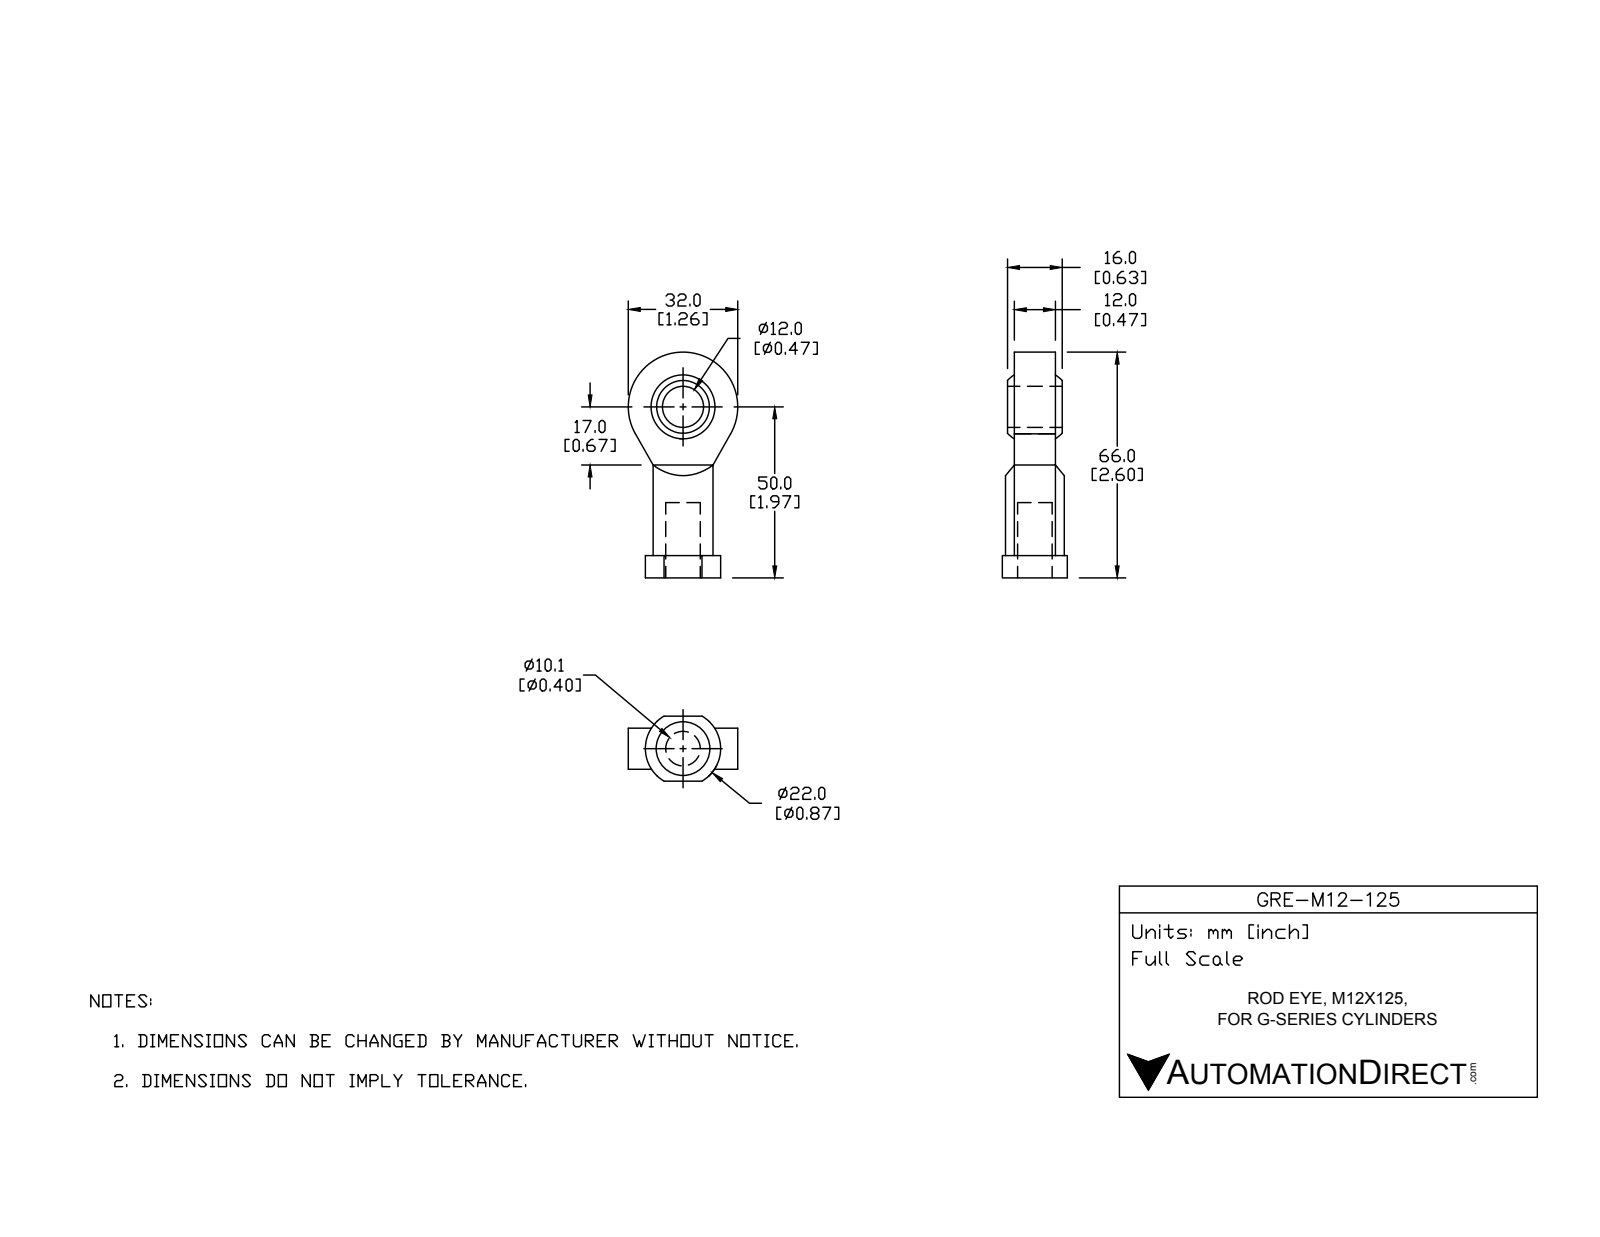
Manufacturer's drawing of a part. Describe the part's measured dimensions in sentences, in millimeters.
The part is named "GRE-M12-125". Its 3-D file was written by "SolidWorks 2017 (AUTOMOTIVE_DESIGN)". It is 1 solid with 36 faces: 11 planar, 9 cylindrical and 16 other. Overall it measures 66 by 31.9 by 19 millimeters. Its volume is 14 666 cubic millimeters and its surface area 6 717 square millimeters. Round holes: 1 of diameter 10.11, 1 of diameter 12. Round bosses or shafts: 1 of diameter 17.3. Partial cylindrical surfaces (rounded edges, fillets, slot ends): 1 of radius 11, 1 of radius 15.95. The main face-to-face distances are 11.8, 3.6, 15.4, 1.5, 17.5, 2.1, 13.9, 19, 16.
